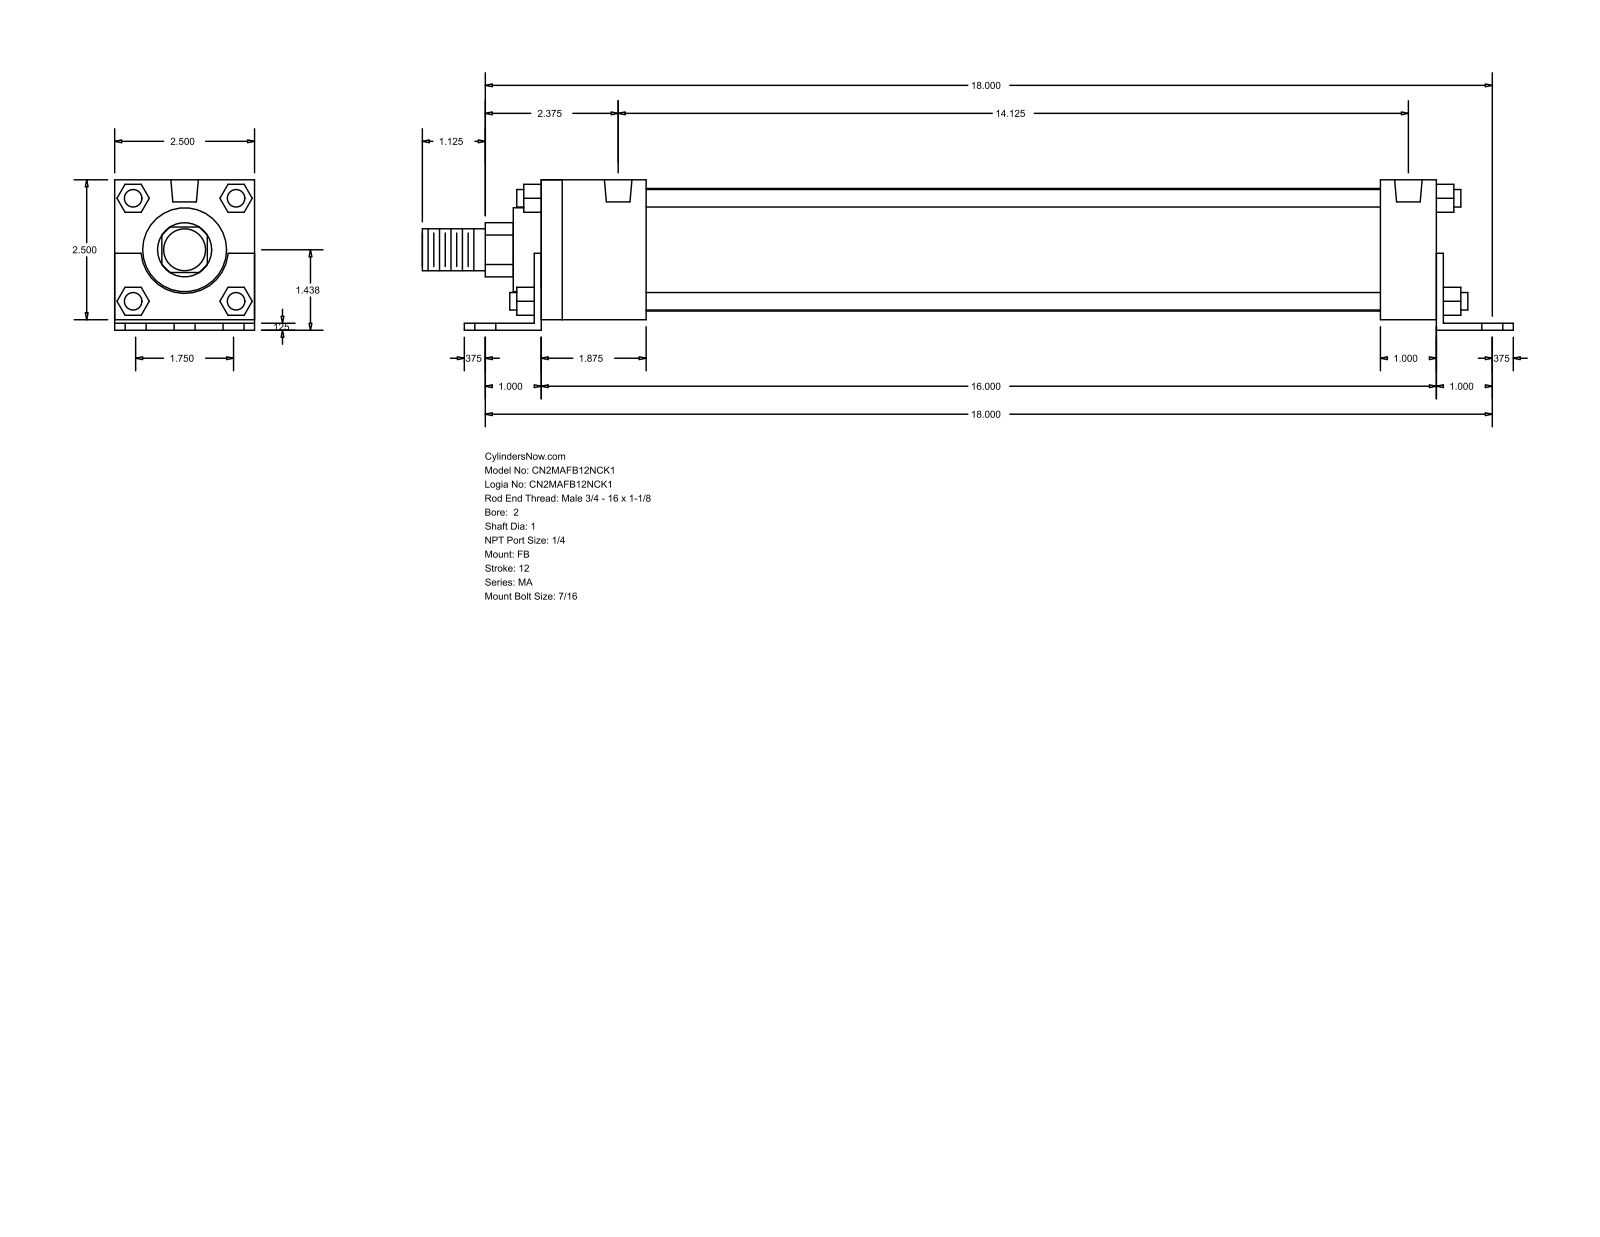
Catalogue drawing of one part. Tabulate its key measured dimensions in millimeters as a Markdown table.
| quantity | value |
| --- | --- |
| part name | MA_FB__0200_1 |
| STEP written by | GSSL Pune (CONFIG_CONTROL_DESIGN) |
| units | millimeters |
| bodies | 0 solids, 140 faces (105 planar, 35 cylindrical, 0 other) |
| overall size | 495.3 × 68.26 × 63.5 |
| round holes (diameter × count) | 11.11 × 6, 7.94 × 4, 12.49 × 2 |
| round bosses / shafts (diameter × count) | 7.94 × 4, 55.63 × 1, 38.1 × 1, 25.4 × 1, 19.05 × 1 |
| partial cylindrical surfaces (radius × count) | 12.29 × 1, 19.81 × 1 |
| main face-to-face distances | 63.5, 3.17, 4.76, 68.26, 1.59, 65.09, 12.7, 3.18, 406.4, 409.58 |
| hole center spacings | 22.23, 457.74, 457.2, 44.11, 44.46, 64.3, 358.77, 397.49 |
